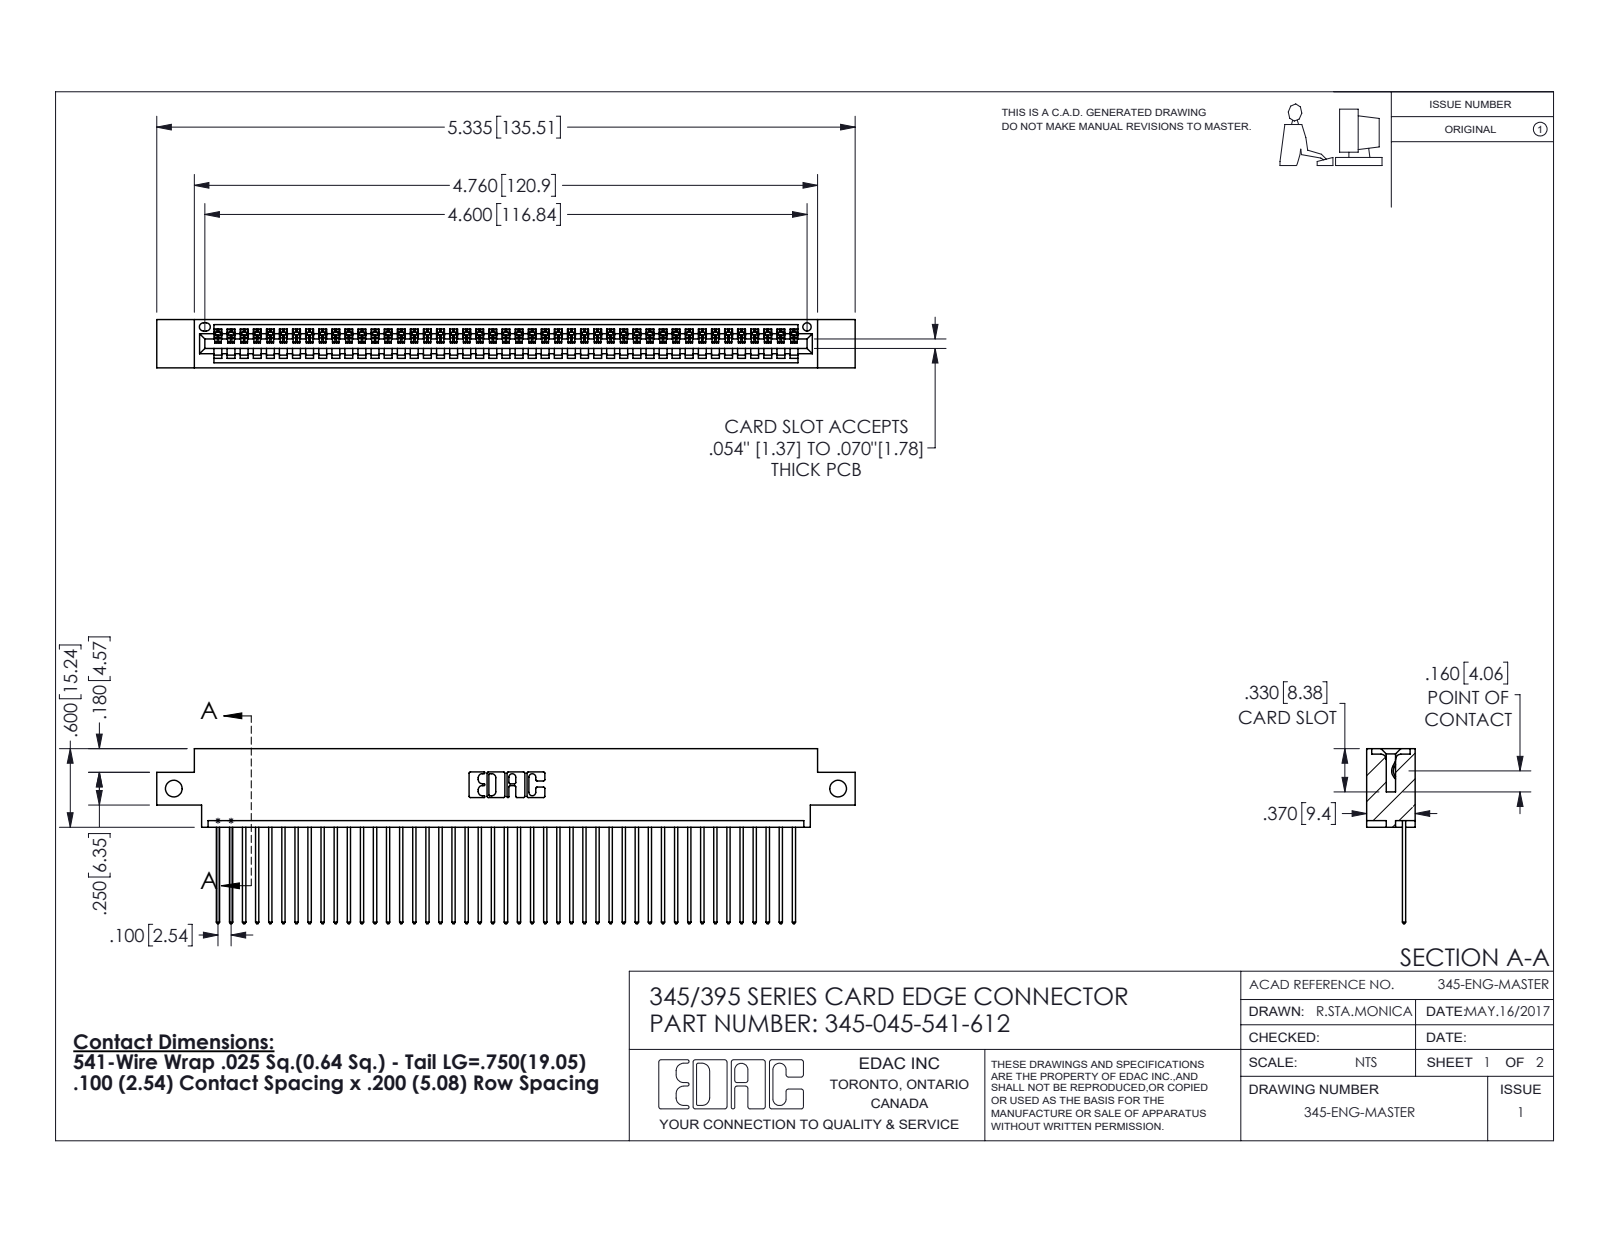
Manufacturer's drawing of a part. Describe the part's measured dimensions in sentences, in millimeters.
The part is named "345 Part_0.170 Offset - Side Mount; 345-292-001_345-293-141; 345-045-541-612". Its 3-D file was written by "SolidWorks 2016 (CONFIG_CONTROL_DESIGN)". It is 46 solids with 2740 faces: 1884 planar, 856 cylindrical and 0 other. Overall it measures 135.5 by 34 by 9.4 millimeters. Its volume is 12 800 cubic millimeters and its surface area 17 970 square millimeters. Round holes: 2 of diameter 3.3, 1 of diameter 1.6. Partial cylindrical surfaces (rounded edges, fillets, slot ends): 90 of radius 0.2, 90 of radius 0.3, 22 of radius 0.3, 6 of radius 0.2, 6 of radius 0.8, 3 of radius 0.7, 2 of radius 0.8, 2 of radius 1. The main face-to-face distances are 1.8, 7.6, 9.4, 2.5, 6.9, 0.6, 5.1, 5.7, 4.4, 3.8. The hole center spacings are 128.9.
